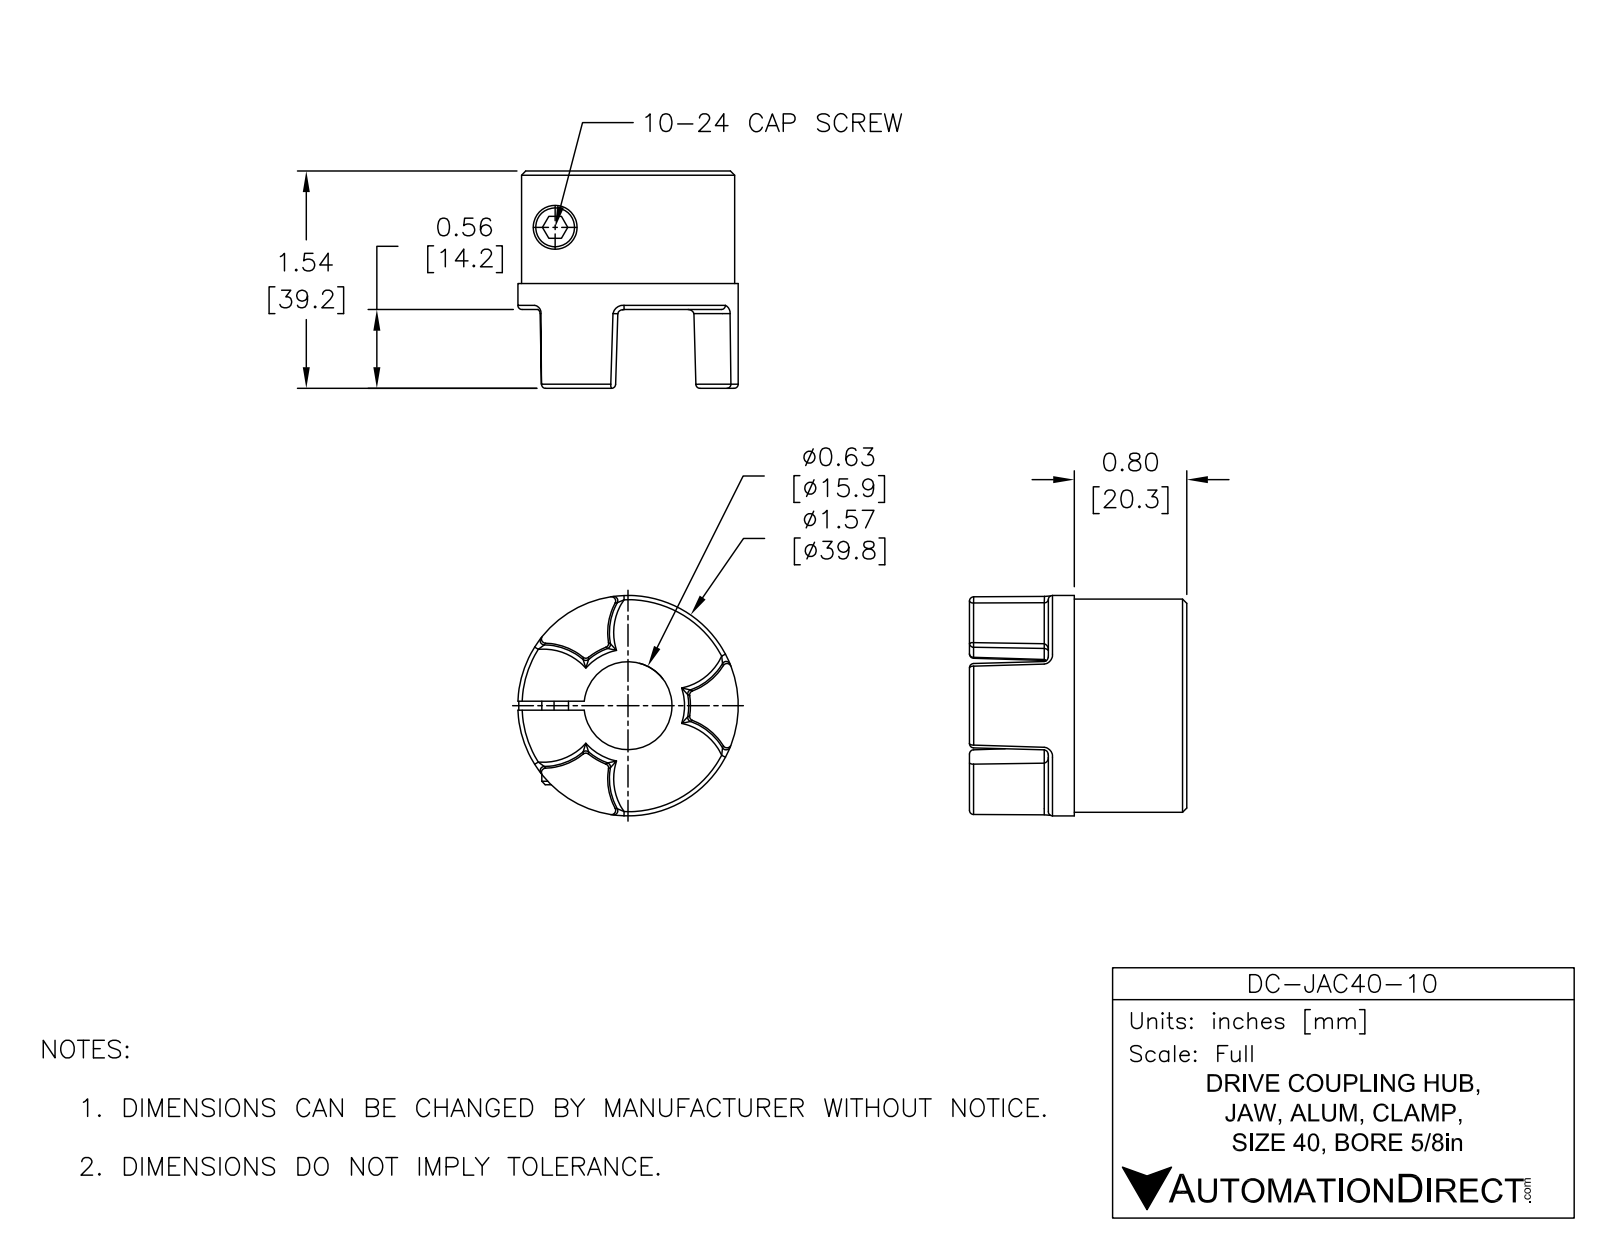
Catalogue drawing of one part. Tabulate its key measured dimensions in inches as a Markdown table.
| quantity | value |
| --- | --- |
| part name | DC-JAC40-10 |
| STEP written by | SolidWorks 2015 (AUTOMOTIVE_DESIGN) |
| units | inches |
| bodies | 1 solid, 109 faces (11 planar, 25 cylindrical, 73 other) |
| overall size | 1.566 × 1.565 × 1.544 |
| volume | 1.639 in³ |
| surface area | 13.5 in² |
| round holes (diameter × count) | 0.201 × 1, 0.329 × 1, 0.625 × 1 |
| round bosses / shafts (diameter × count) | 1.566 × 1, 1.515 × 1 |
| partial cylindrical surfaces (radius × count) | 0.03 × 6, 0.445 × 2, 0.491 × 1 |
| main face-to-face distances | 0.984, 0.063, 1.544, 0.56, 0.799, 0.185, 0.745, 0.157, 0.22 |
